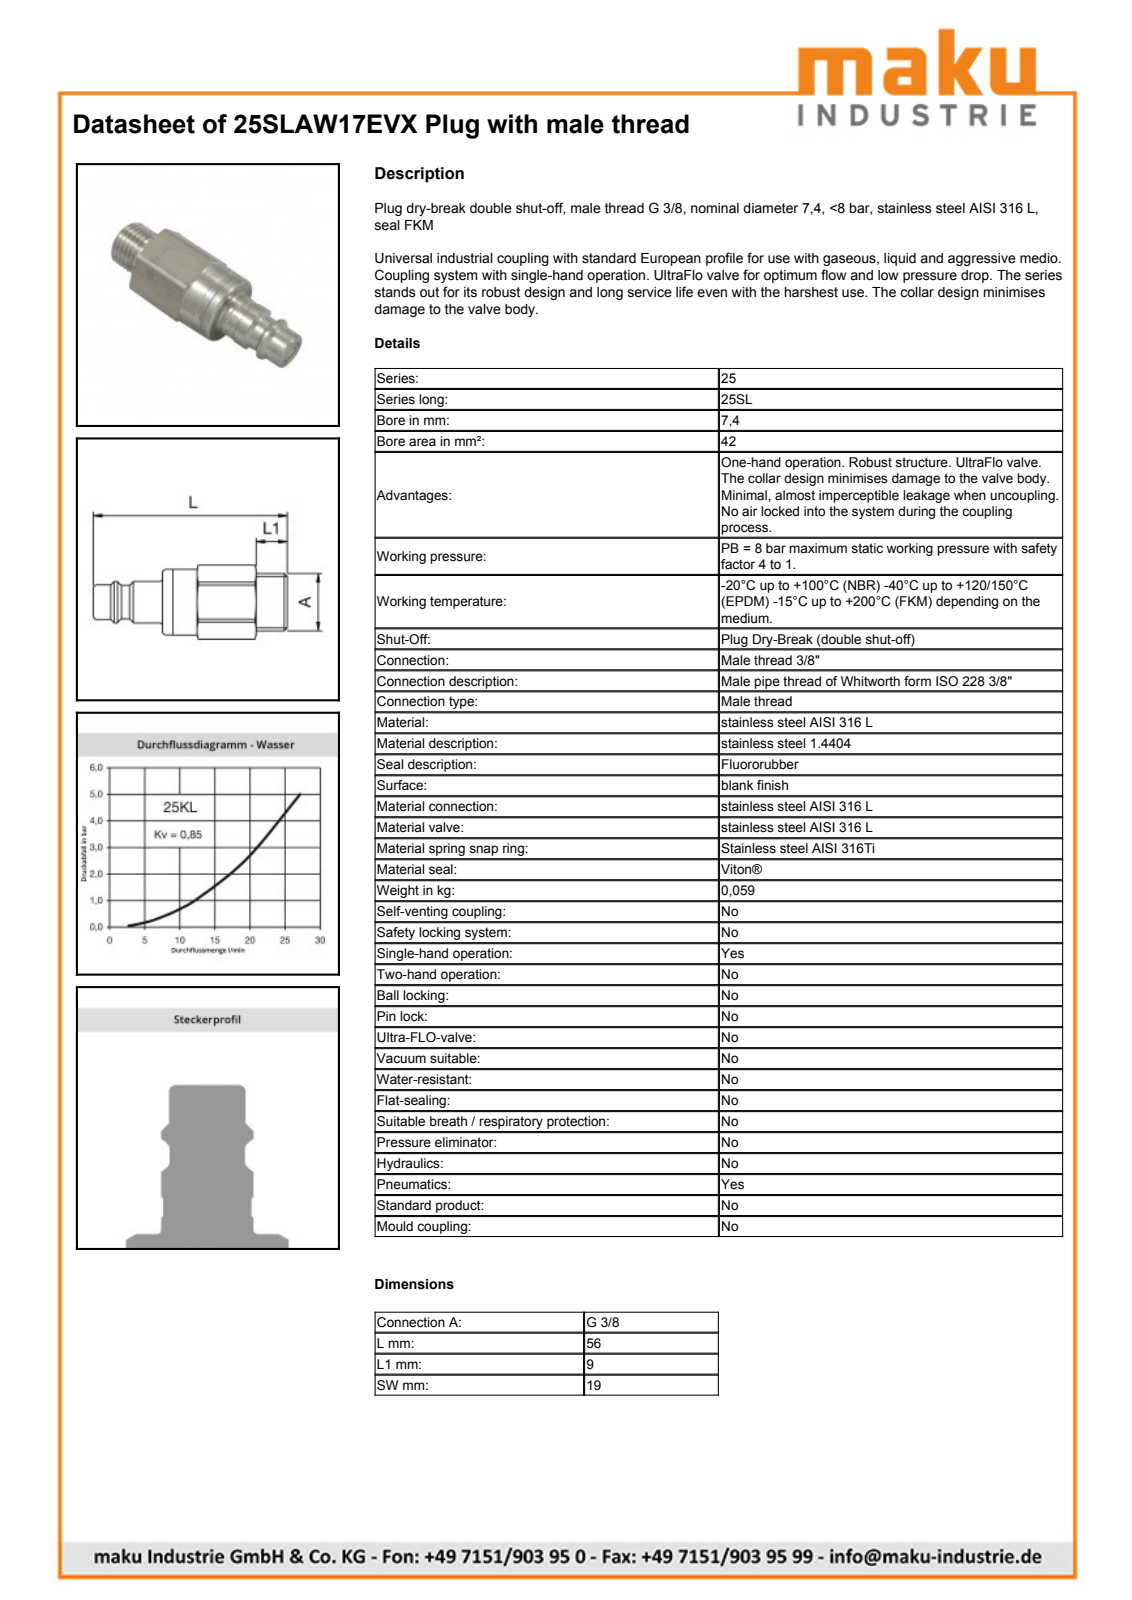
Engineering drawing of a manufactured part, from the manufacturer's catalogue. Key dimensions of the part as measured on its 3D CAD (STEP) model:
Part name (STEP PRODUCT): D112165
STEP written by: Autodesk Inventor 2013 (AUTOMOTIVE_DESIGN)
Units: millimetres
Bodies: 1 solid, 63 faces (16 planar, 20 cylindrical, 27 other)
Overall size (bounding box): 56 × 21.24 × 20.37
Volume: 10 552 mm³ · Surface area: 5 951 mm²
Round holes (diameter × count): ⌀7.85 ×1, ⌀9.5 ×1, ⌀14 ×1, ⌀15.1 ×1, ⌀16 ×1
Round bosses / shafts (diameter × count): ⌀19 ×1, ⌀18.95 ×1, ⌀16.66 ×1, ⌀14.5 ×1, ⌀12 ×1, ⌀9.9 ×1, ⌀9.75 ×1
Partial cylindrical surfaces — rounded edges, fillets, slot ends (radius × count): R10.7 ×1
Main face-to-face distances: 19, 36, 3, 20, 56, 24, 19.5, 47, 27, 9
